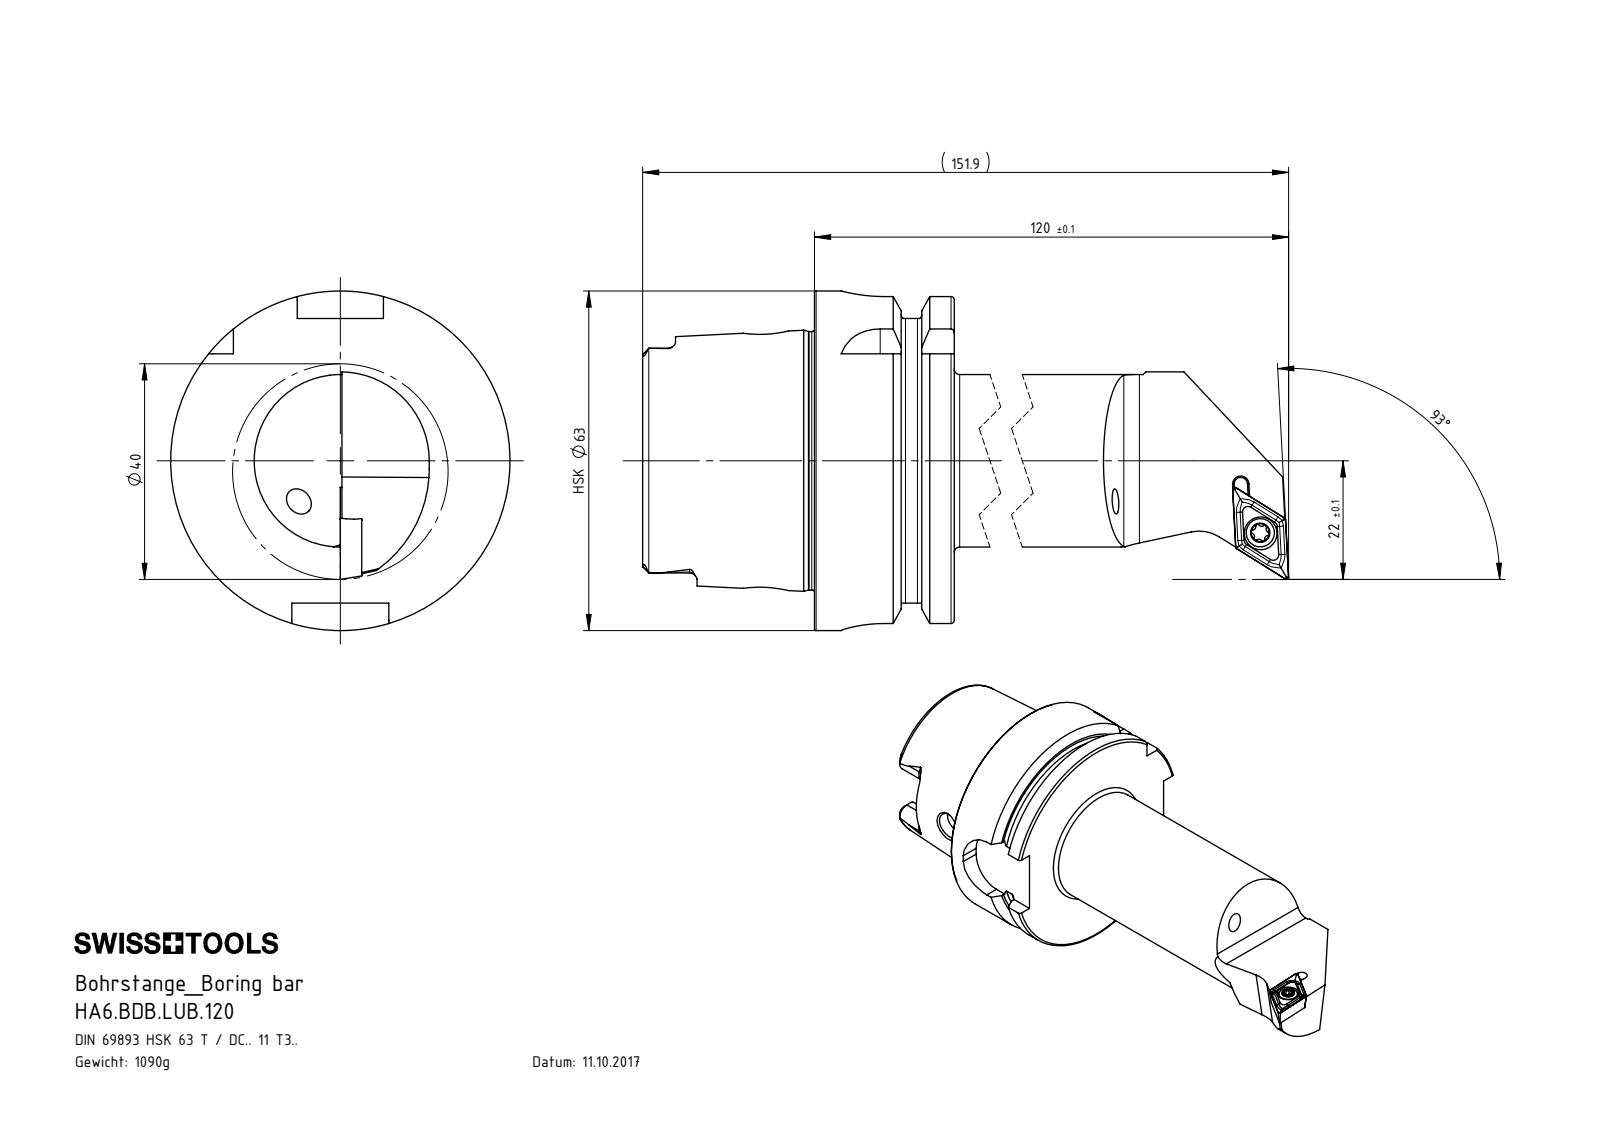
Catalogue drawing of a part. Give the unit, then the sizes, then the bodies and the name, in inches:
Units: inches
Overall size (bounding box): 5.98 × 2.48 × 2.48
Round holes (diameter × count): ⌀0.165 ×2, ⌀0.13 ×1, ⌀0.157 ×1, ⌀0.173 ×1, ⌀0.24 ×1, ⌀0.295 ×1, ⌀0.331 ×1, ⌀0.394 ×1, ⌀0.669 ×1, ⌀0.748 ×1, ⌀1.339 ×1, ⌀1.575 ×1
Round bosses / shafts (diameter × count): ⌀2.48 ×1, ⌀2.163 ×1, ⌀1.887 ×1, ⌀1.26 ×1, ⌀0.207 ×1, ⌀0.197 ×1, ⌀0.157 ×1
Partial cylindrical surfaces — rounded edges, fillets, slot ends (radius × count): R0.013 ×6, R0.023 ×6, R0.055 ×6, R0.315 ×4, R0.111 ×2, R0.113 ×2, R0.049 ×1, R0.118 ×1
Main face-to-face distances: 1.022, 0.63, 0.392, 1.256, 1.648, 2.278, 2.079, 0.858, 0.467, 2.114
Hole centre spacings: 4.274, 4.277
Volume: 8.458 in³ · Surface area: 51.66 in²
Bodies: 5 solids, 307 faces (80 planar, 88 cylindrical, 139 other)
Part name (STEP PRODUCT): DCMT11T304; HA6-BDB.LUB.120; KVT_MB_600_050; WCB-ER2.001.009_A (+1 more)
STEP written by: SolidWorks 2017 (AUTOMOTIVE_DESIGN)
